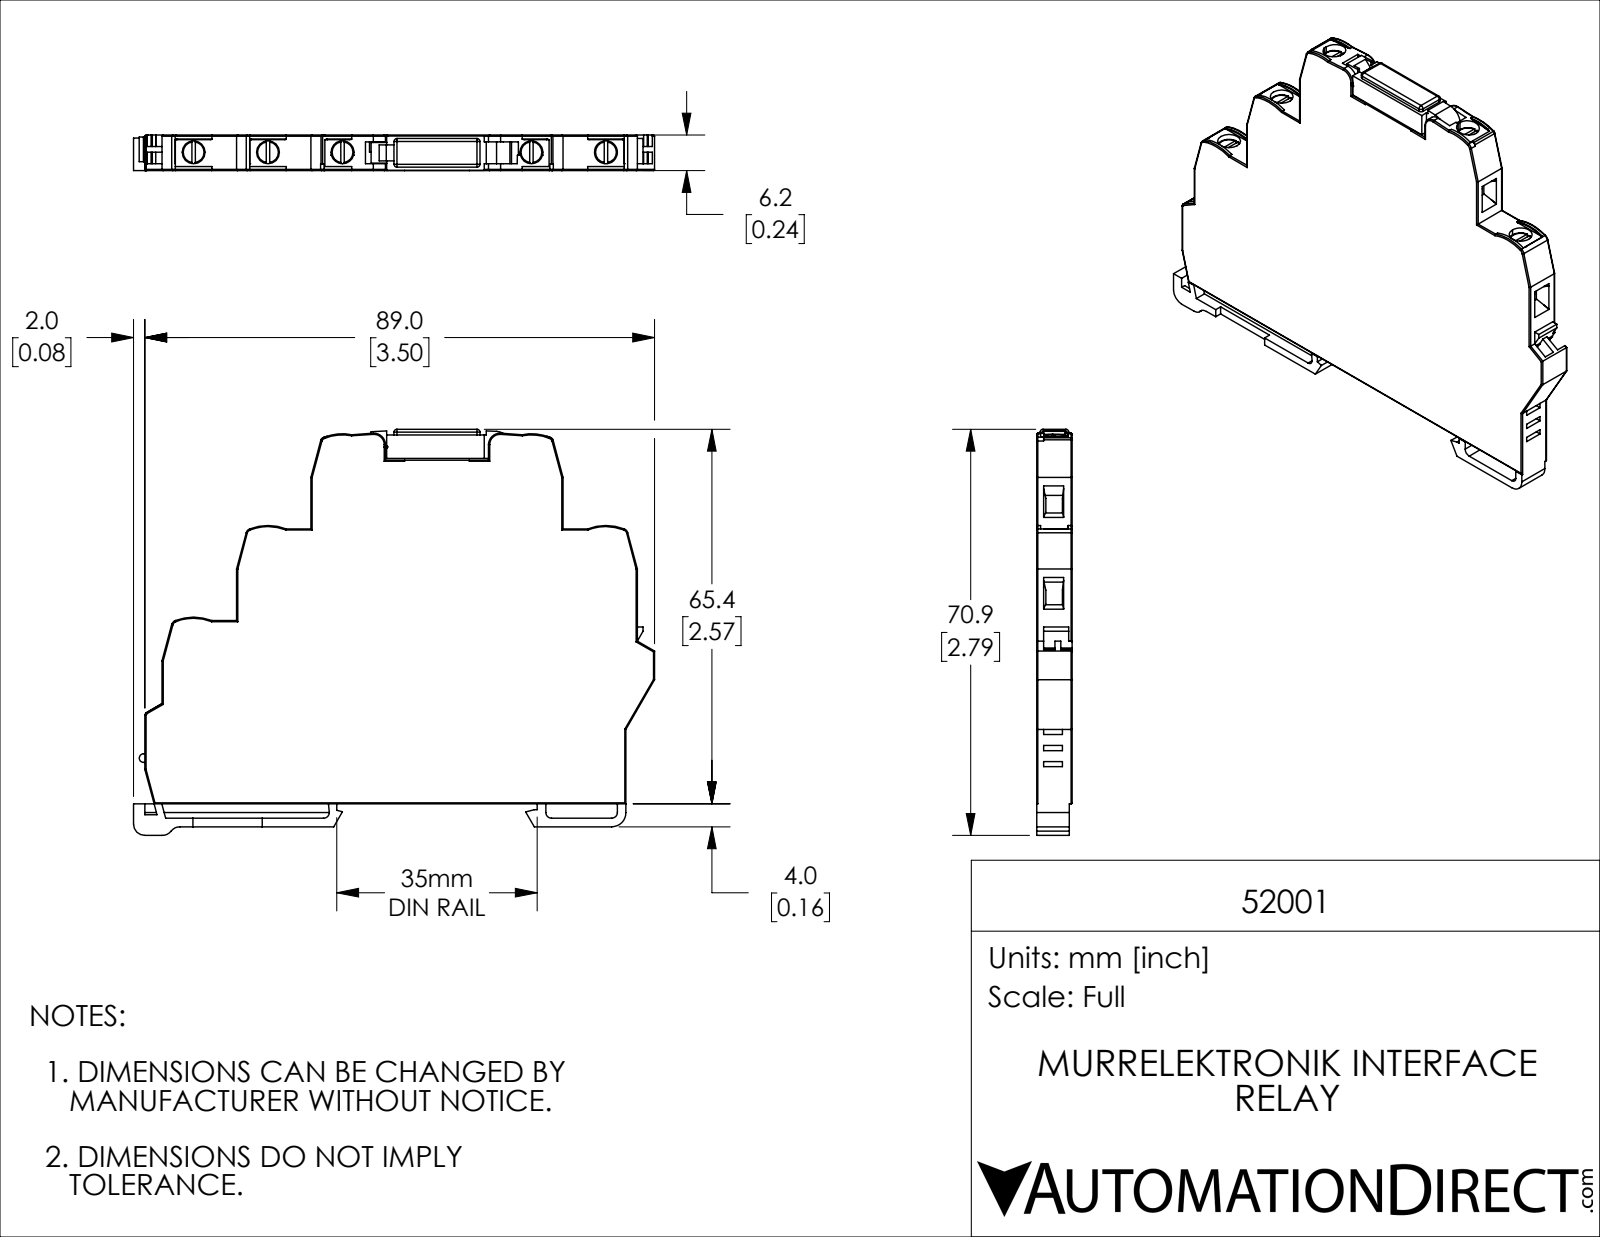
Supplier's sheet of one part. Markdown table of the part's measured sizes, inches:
| quantity | value |
| --- | --- |
| part name | 52001 |
| STEP written by | SolidWorks 2019 (CONFIG_CONTROL_DESIGN) |
| units | inches |
| bodies | 2 solids, 566 faces (351 planar, 147 cylindrical, 68 other) |
| overall size | 3.583 × 2.791 × 0.244 |
| volume | 1.706 in³ |
| surface area | 20.13 in² |
| round holes (diameter × count) | 0.157 × 5, 0.075 × 1 |
| round bosses / shafts (diameter × count) | 0.079 × 1 |
| partial cylindrical surfaces (radius × count) | 0.008 × 56, 0.02 × 11, 0.039 × 8, 0.079 × 6, 0.03 × 5, 0.346 × 5, 0.005 × 4, 0.016 × 3 |
| main face-to-face distances | 0.244, 0.059, 0.197, 0.098, 0.157, 0.118, 0.047, 0.02, 0.039, 2.362 |
| hole center spacings | 0.512, 1.811, 2.323, 1.024, 1.299, 2.835 |
